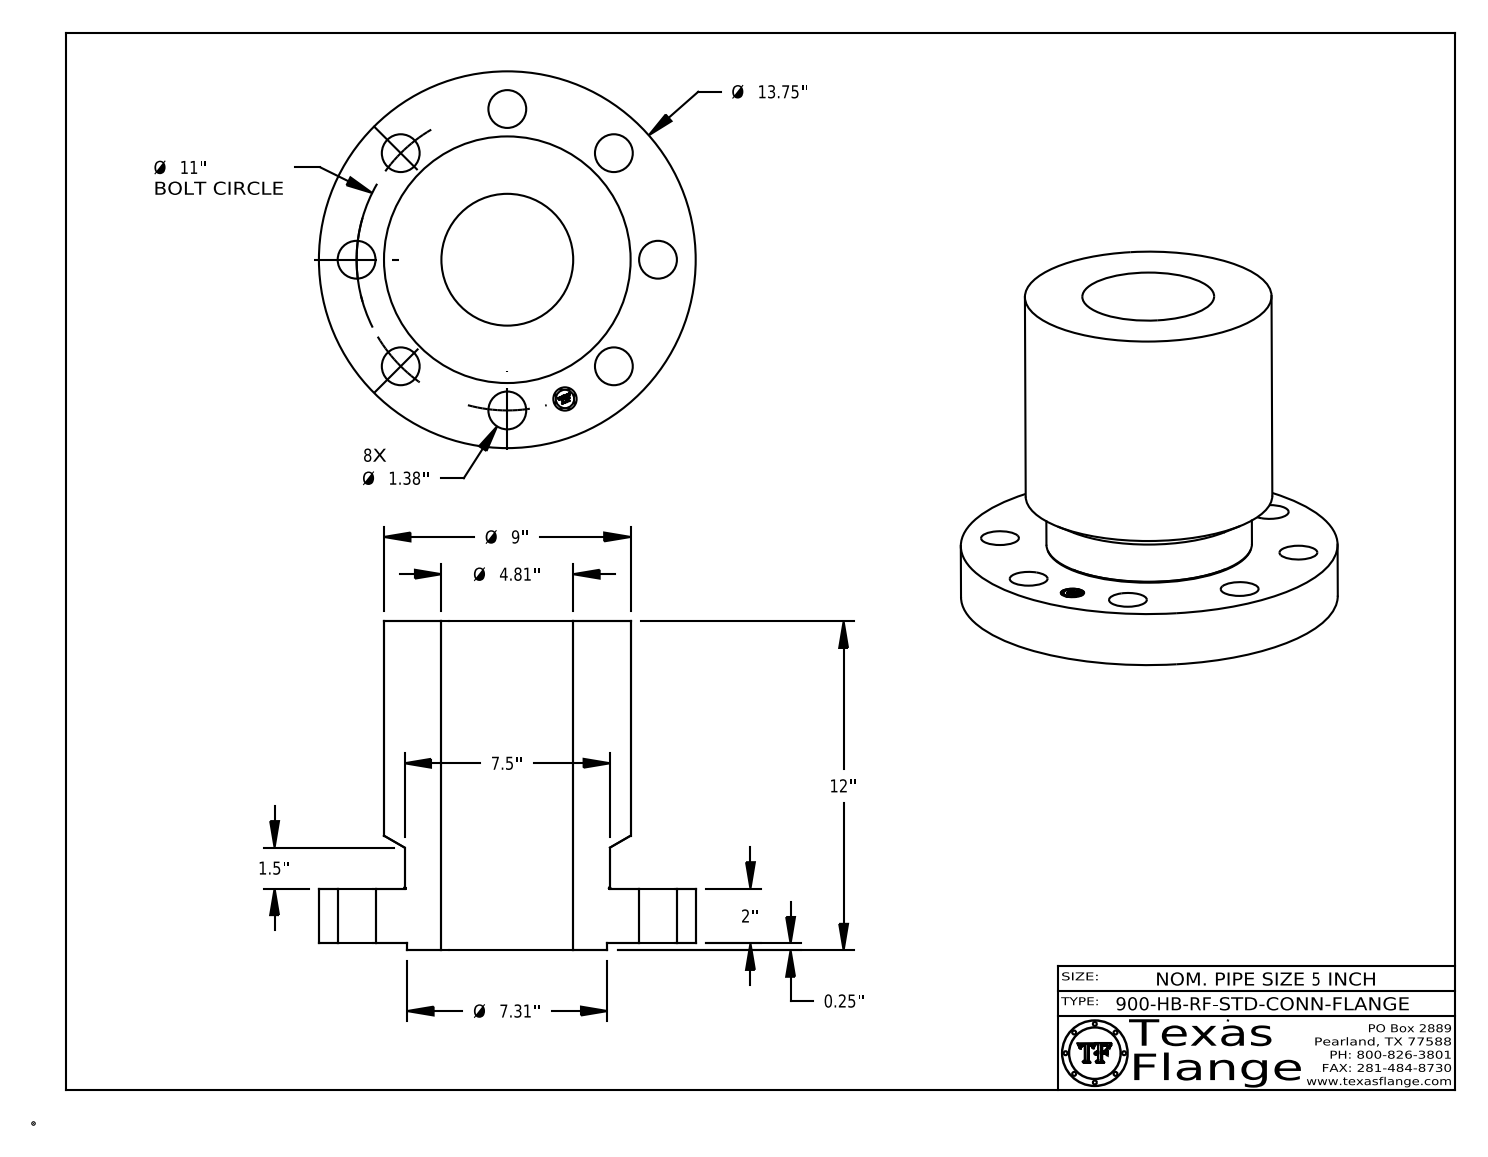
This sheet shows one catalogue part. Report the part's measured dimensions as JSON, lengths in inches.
{"part_name": "5-900-HB-RF-STD-CONN-FLANGE", "step_written_by": "CATIA V5 STEP AP214 (AUTOMOTIVE_DESIGN)", "units": "inches", "bodies": {"solids": 1, "faces": 421, "planar": 369, "cylindrical": 46, "other": 6}, "overall_size": [13.75, 13.75, 12], "volume_in3": 652.2, "surface_area_in2": 878.8, "round_holes": [[1.38, 8], [0.85, 1], [4.81, 1]], "round_bosses_or_shafts": [[0.051, 8], [13.75, 1], [9, 1], [7.5, 1], [7.31, 1], [0.67, 1]], "face_to_face_distances": [2, 11.75, 9.75, 0.25, 2.25, 12, 2.245, 1.995, 9.755, 0.254], "hole_center_spacings": [5.5, 4.209, 10.163, 7.778, 7.778, 2.146, 9.146, 11]}
